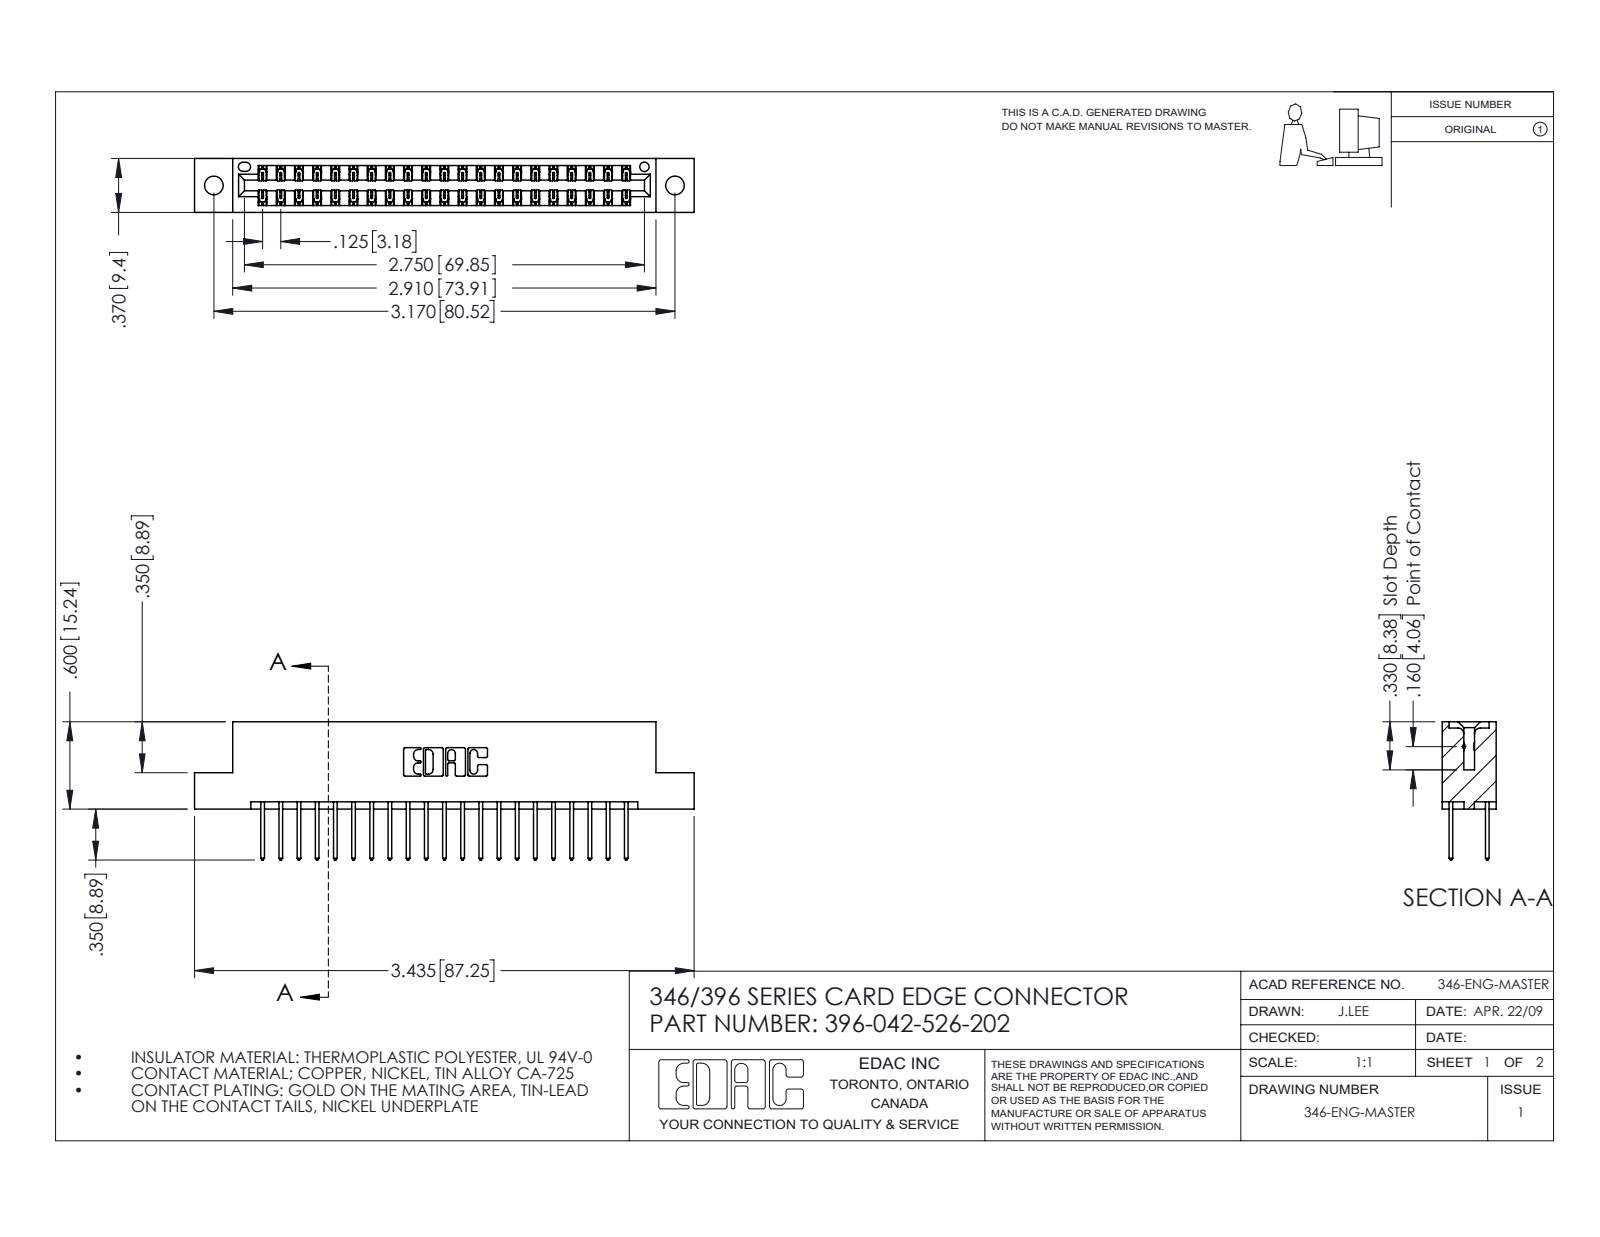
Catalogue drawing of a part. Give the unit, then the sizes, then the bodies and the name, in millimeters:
Units: millimetres
Overall size (bounding box): 87.2 × 24.1 × 9.4
Round holes (diameter × count): ⌀3.3 ×2, ⌀1.6 ×1
Partial cylindrical surfaces — rounded edges, fillets, slot ends (radius × count): R0.2 ×63, R0.3 ×42, R0.3 ×22, R0.2 ×6, R0.8 ×6, R0.7 ×3, R0.4 ×2, R0.6 ×2
Main face-to-face distances: 1.2, 8.2, 6.4, 9.4, 1.8, 7.6, 0.6, 7, 3.8, 5.6
Hole centre spacings: 6.2, 75.3, 80.5
Volume: 8 370 mm³ · Surface area: 11 230 mm²
Bodies: 43 solids, 2306 faces (1546 planar, 760 cylindrical, 0 other)
Part name (STEP PRODUCT): 345-292-001_345-293-126; 346 Part_Flush Mounting Lugs - 0.128 Dia; 396-042-526-202
STEP written by: SolidWorks 2016 (CONFIG_CONTROL_DESIGN)
